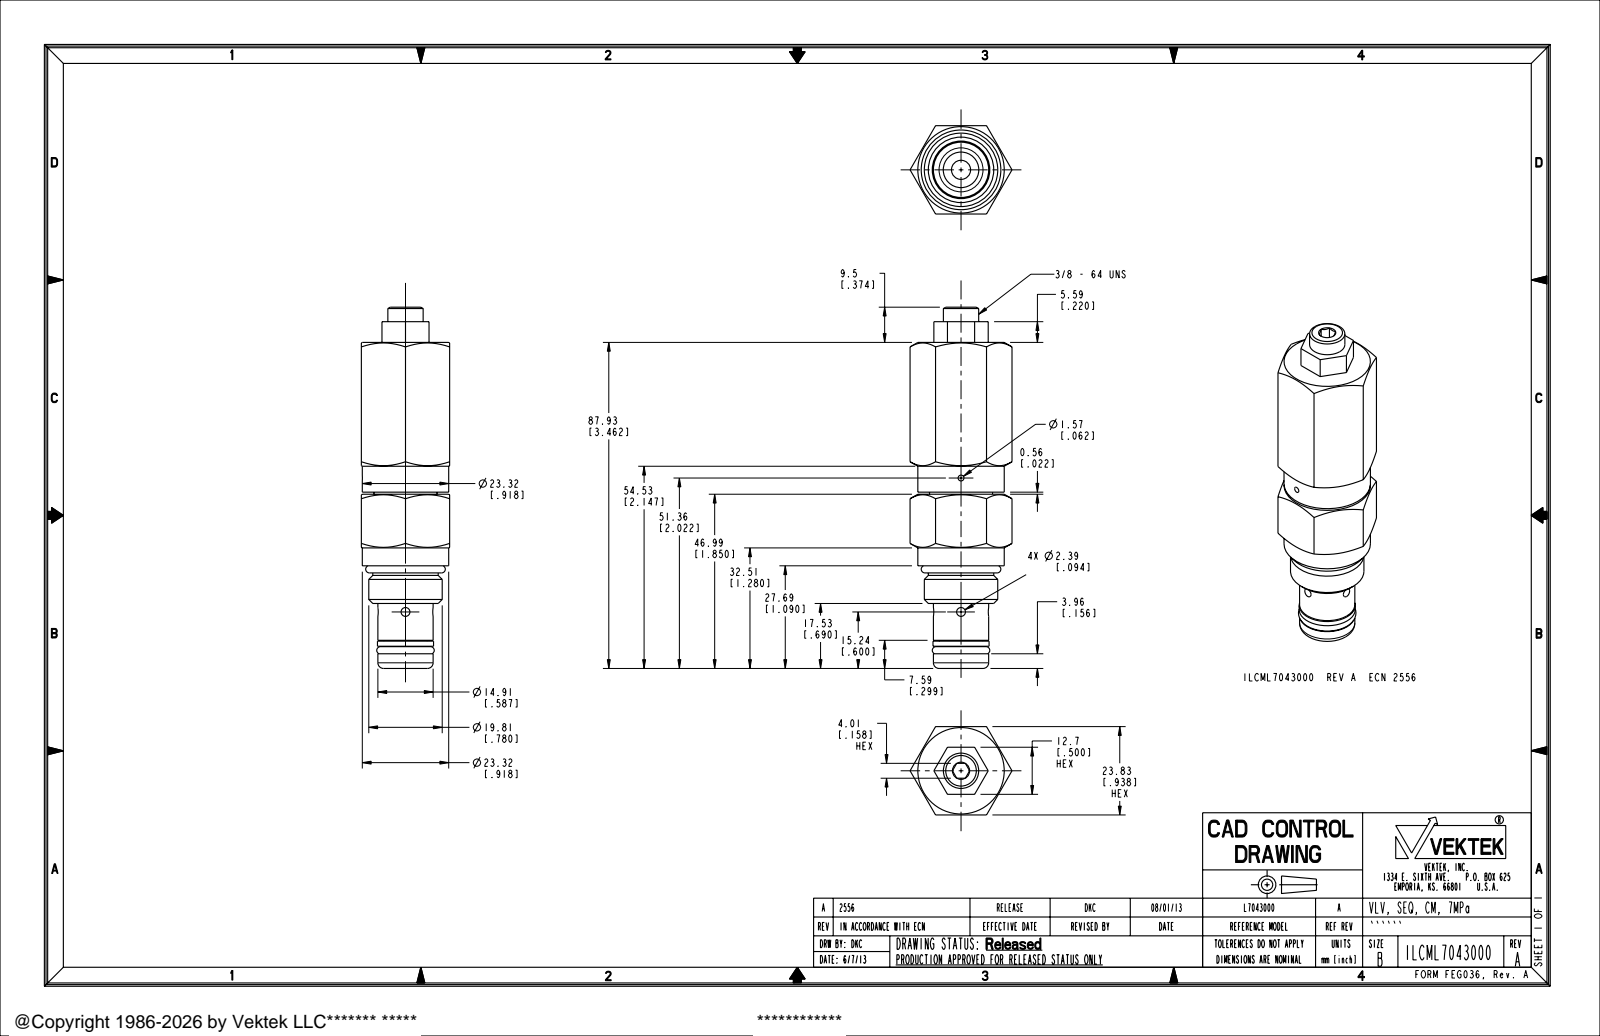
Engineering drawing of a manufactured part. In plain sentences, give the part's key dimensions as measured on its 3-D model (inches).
The part is named "ILCML7043000". Its 3-D file was written by "PRO/ENGINEER BY PARAMETRIC TECHNOLOGY CORPORATION, 2007460 (AUTOMOTIVE_DESIGN_CC2)". It is 1 solid with 112 faces: 42 planar, 40 cylindrical and 30 other. Overall it measures 3.836 by 1.083 by 0.938 inches. Its volume is 2.15 cubic inches and its surface area 14.08 square inches. Round holes: 2 of diameter 0.094, 1 of diameter 0.062, 1 of diameter 0.203, 1 of diameter 0.378. Round bosses or shafts: 1 of diameter 0.918, 1 of diameter 0.78, 1 of diameter 0.695, 1 of diameter 0.67, 1 of diameter 0.596, 1 of diameter 0.587, 1 of diameter 0.46, 1 of diameter 0.375. The main face-to-face distances are 0.938, 0.219, 0.719, 1.612, 0.022, 1.59, 0.4, 0.76, 0.782, 2.372. The hole center spacings are 1.422.
